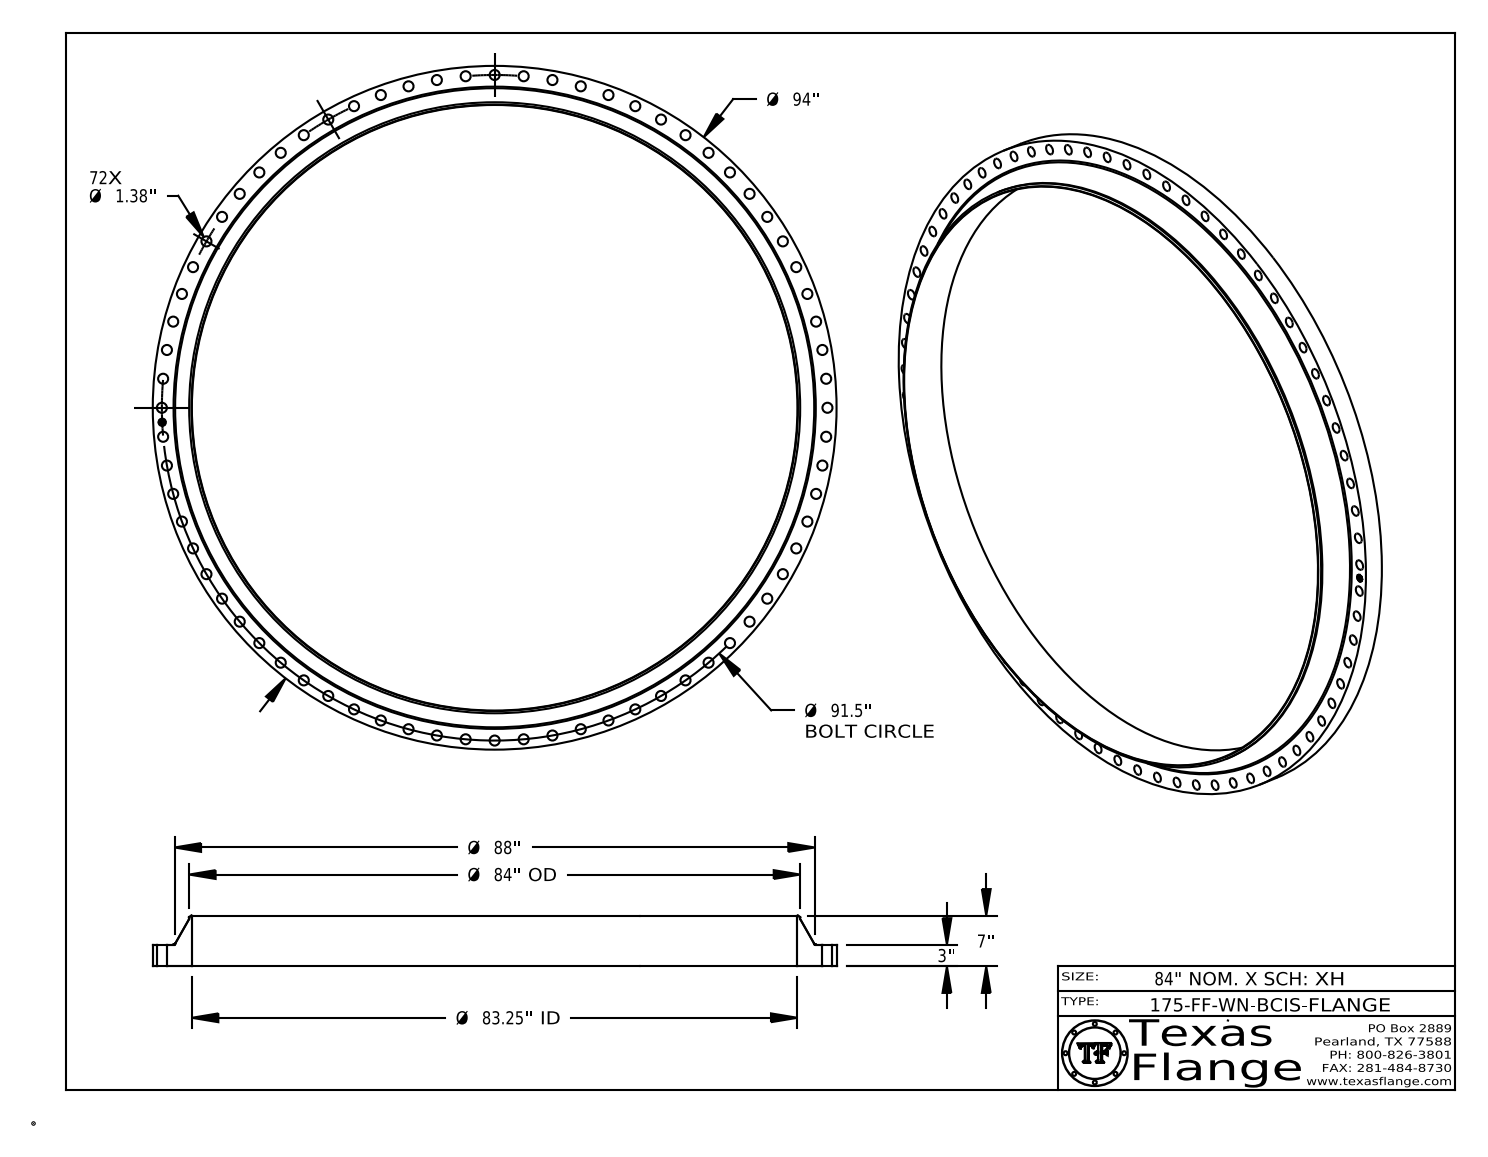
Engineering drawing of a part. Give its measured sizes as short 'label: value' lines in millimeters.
name: 175-FF-WN, BCIS
written by: CATIA V5 STEP AP214 (AUTOMOTIVE_DESIGN)
unit: mm
bodies: 1 solid, 544 faces (368 planar, 170 cylindrical, 6 other)
size: 2387.6 × 2387.6 × 177.8
volume: 90 060 000 mm³; area: 4 556 000 mm²
holes: 72× ⌀35.1, 1× ⌀25.4, 1× ⌀2114.6
bosses: 8× ⌀1.5, 1× ⌀2387.6, 1× ⌀2133.6, 1× ⌀20
face distances: 76.2, 177.8, 101.6, 0.4, 75.8, 102, 7.6, 7.4, 1.4, 4.9
hole spacings: 1162.1, 2315.3, 101.4, 2288.8, 503, 2304.2, 2321.9, 2216.5
